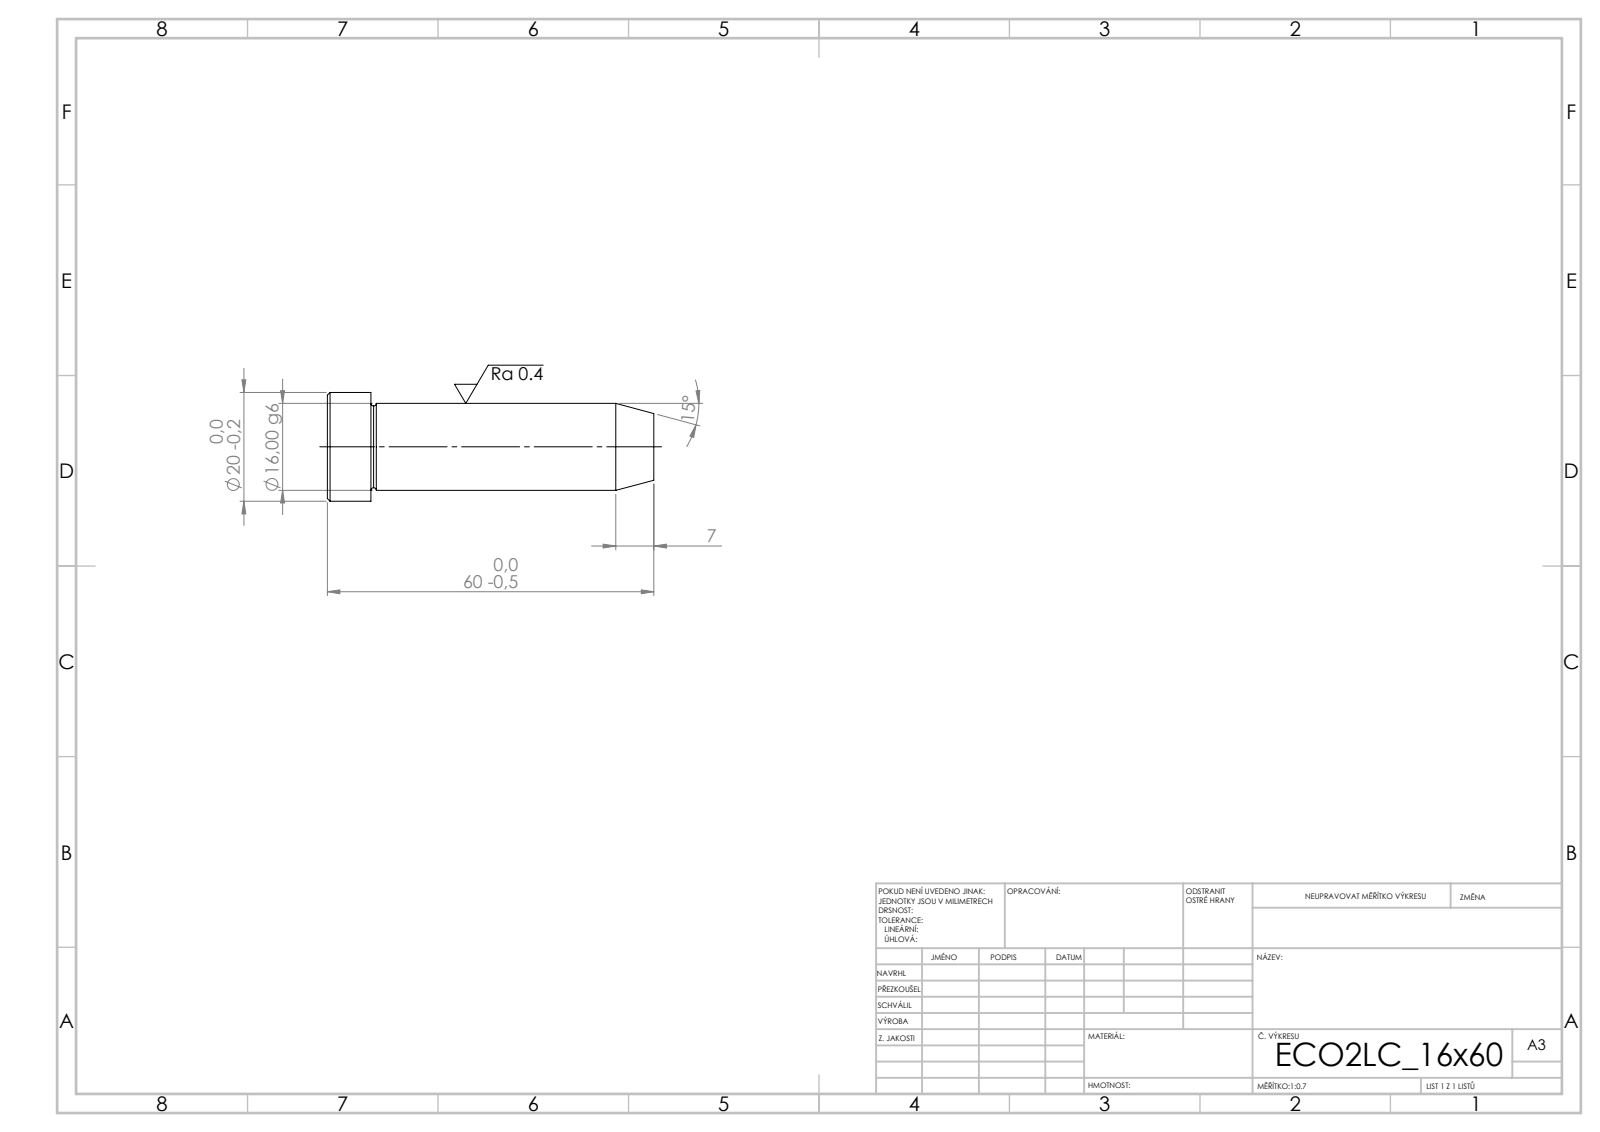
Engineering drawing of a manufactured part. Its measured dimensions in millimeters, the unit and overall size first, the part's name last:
Units: millimetres
Overall size (bounding box): 60 × 20 × 20
Round bosses / shafts (diameter × count): ⌀20 ×1, ⌀16 ×1
Main face-to-face distances: 60, 52, 8
Volume: 12 637 mm³ · Surface area: 3 638 mm²
Bodies: 1 solid, 15 faces (3 planar, 4 cylindrical, 8 other)
STEP written by: SolidWorks 2019 (CONFIG_CONTROL_DESIGN)
